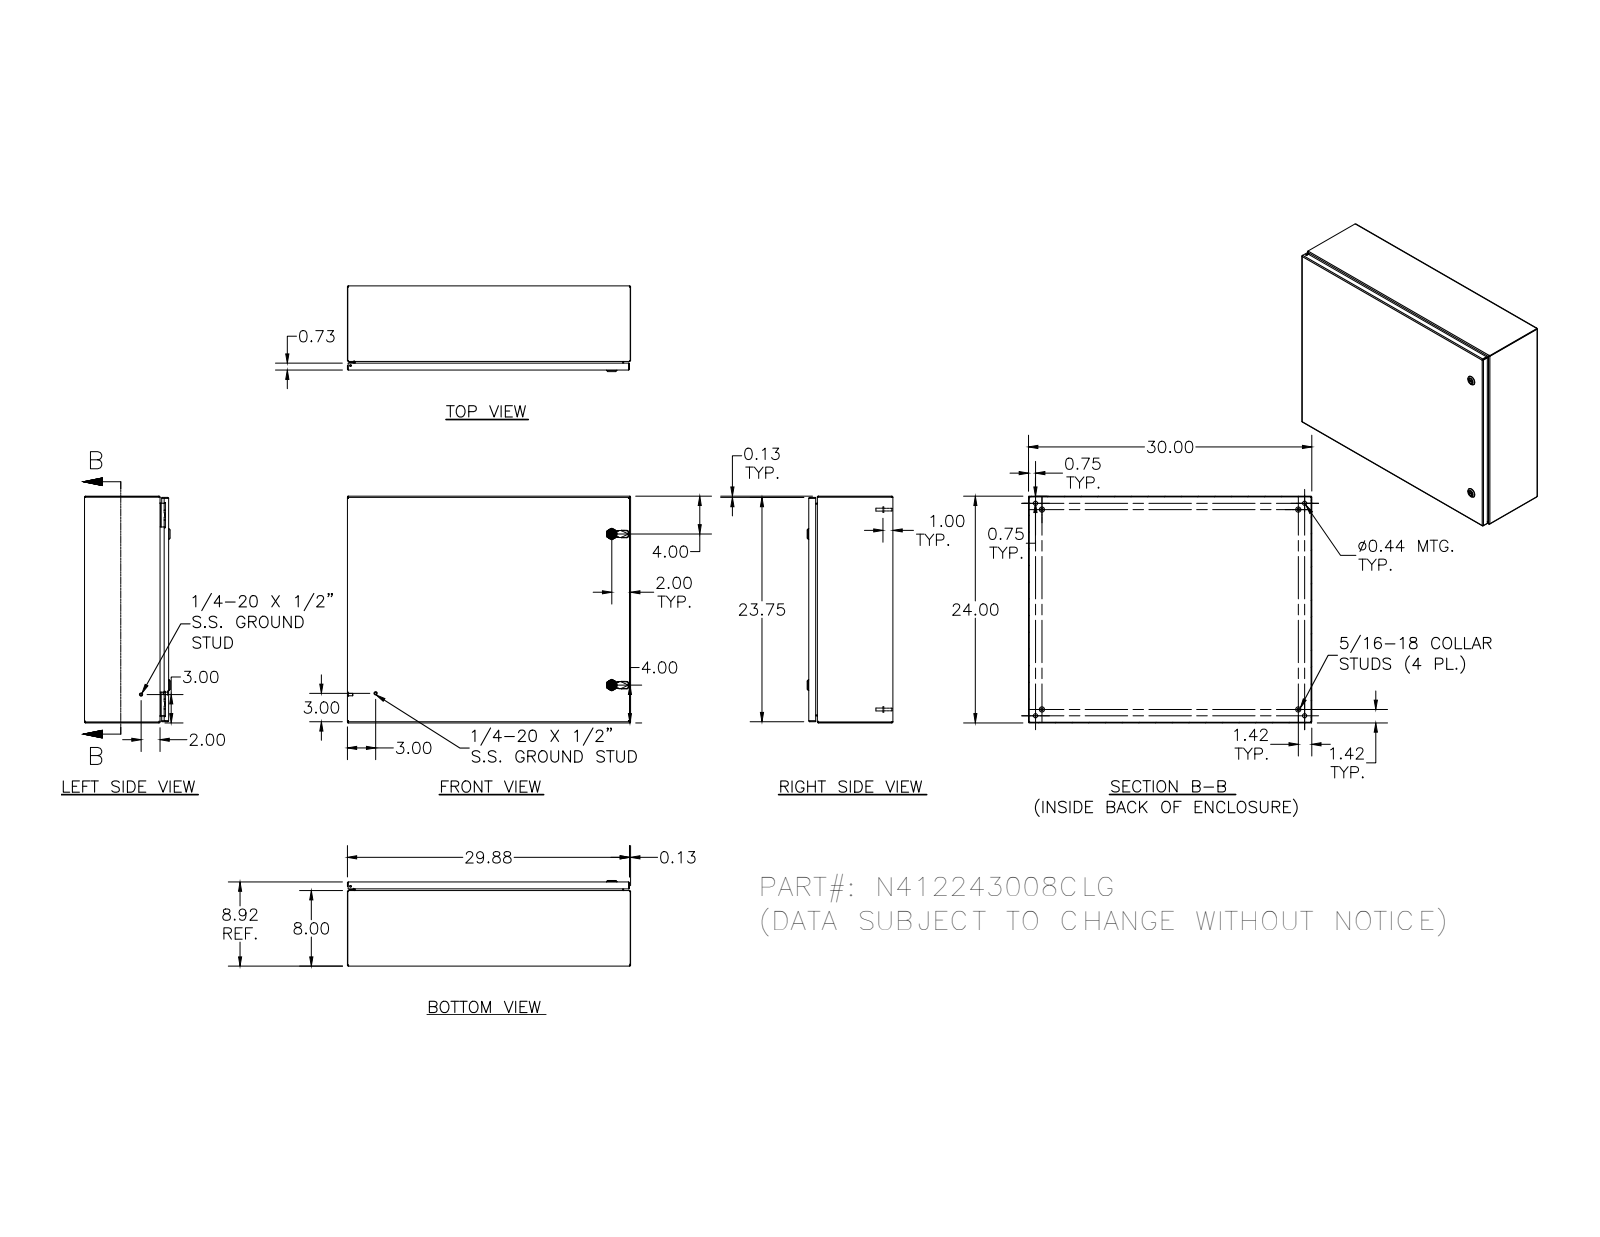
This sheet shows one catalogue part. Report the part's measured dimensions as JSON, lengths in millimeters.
{"part_name": "N412243008C; N4122430CLID; 35124; 1000-u155_asm (+8 more)", "step_written_by": "Autodesk Inventor 2011 (AUTOMOTIVE_DESIGN)", "units": "millimeters", "bodies": {"solids": 38, "faces": 1816, "planar": 706, "cylindrical": 678, "other": 432}, "overall_size": [762, 609.6, 230.5], "volume_mm3": 3055000, "surface_area_mm2": 3274000, "round_holes": [[4.8, 5], [2.4, 4], [3.9, 4], [4.2, 4], [4.4, 4], [11.1, 4], [4, 2], [5, 2], [8, 2], [10, 2], [10.2, 2], [16.1, 2]], "round_bosses_or_shafts": [[6.4, 10], [3.3, 5], [14.3, 4], [9.1, 4], [8.1, 4], [7.6, 4], [7, 4], [6.5, 4]], "partial_cylinders_radius": [[0.3, 54], [0.8, 30], [1.3, 26], [0.5, 23], [2.7, 20], [0.4, 18], [3.2, 16], [0.8, 8]], "face_to_face_distances": [1.9, 224.6, 222.7, 226.5, 1.9, 607.7, 605.8, 609.6, 607.7, 760.1], "hole_center_spacings": [508, 16.8, 16.7, 33.2, 49.9, 491.2, 507.9, 524.7]}
